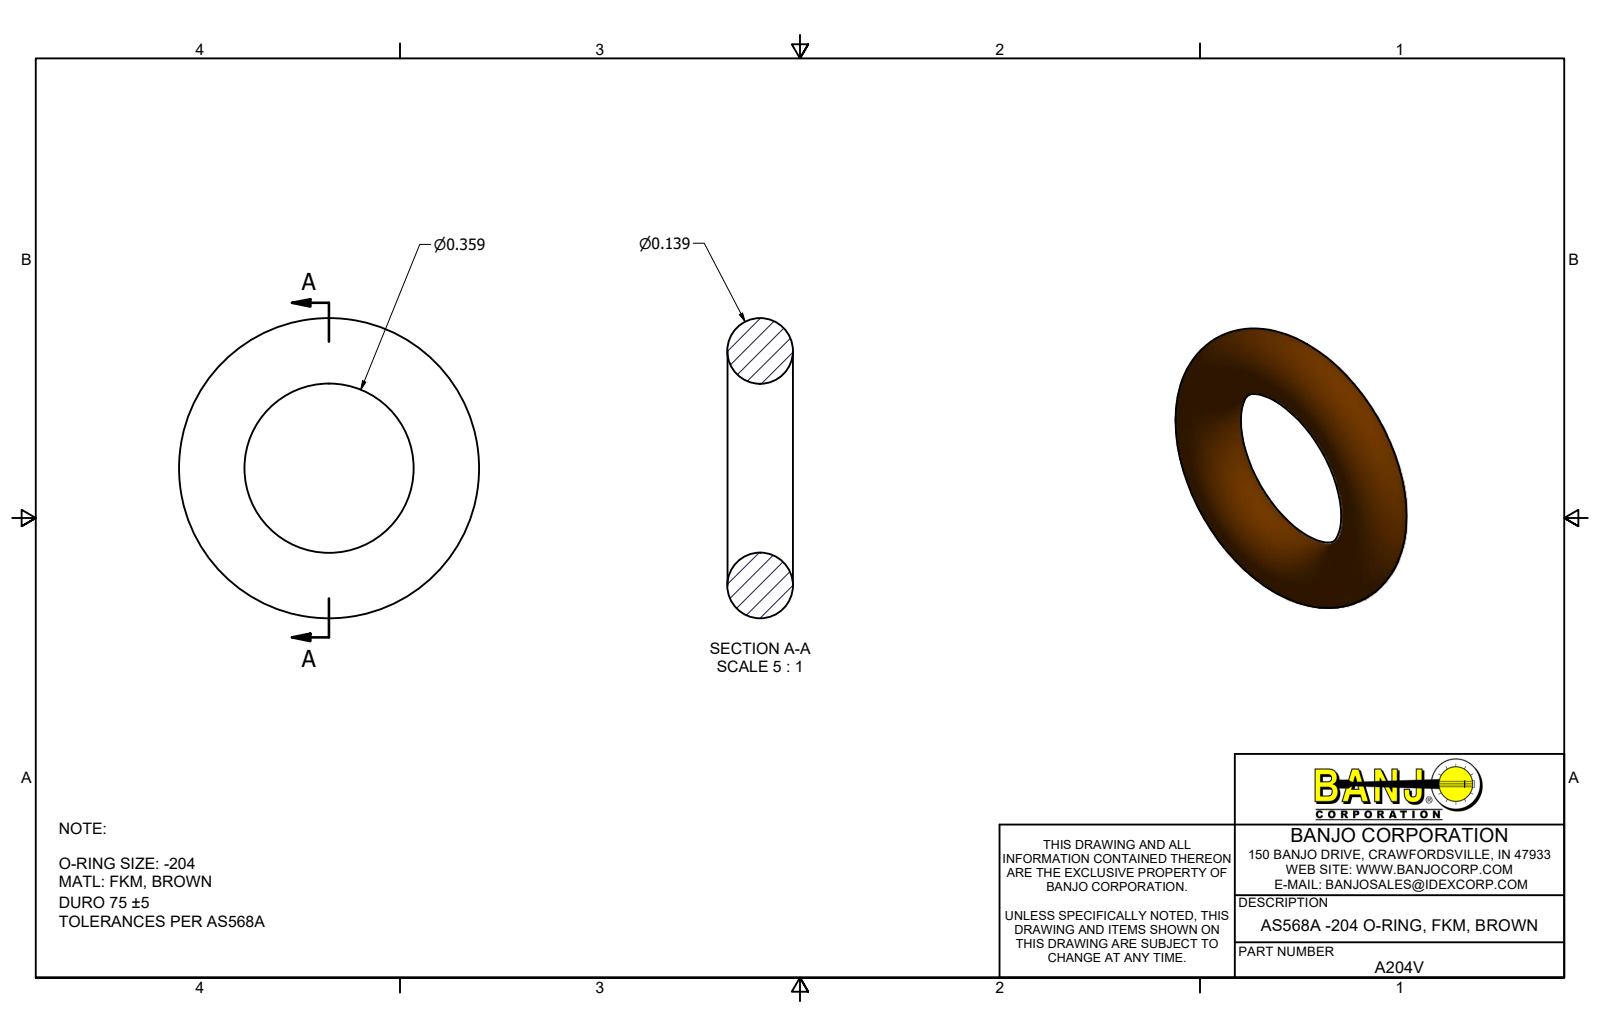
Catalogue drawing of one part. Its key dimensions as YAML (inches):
part_name: "A204V"
step_written_by: "Autodesk Inventor 2019 (AUTOMOTIVE_DESIGN)"
units: inches
bodies: {solids: 1, faces: 1, planar: 0, cylindrical: 0, other: 1}
overall_size: [0.637, 0.637, 0.139]
volume: 0.024
surface_area: 0.683
